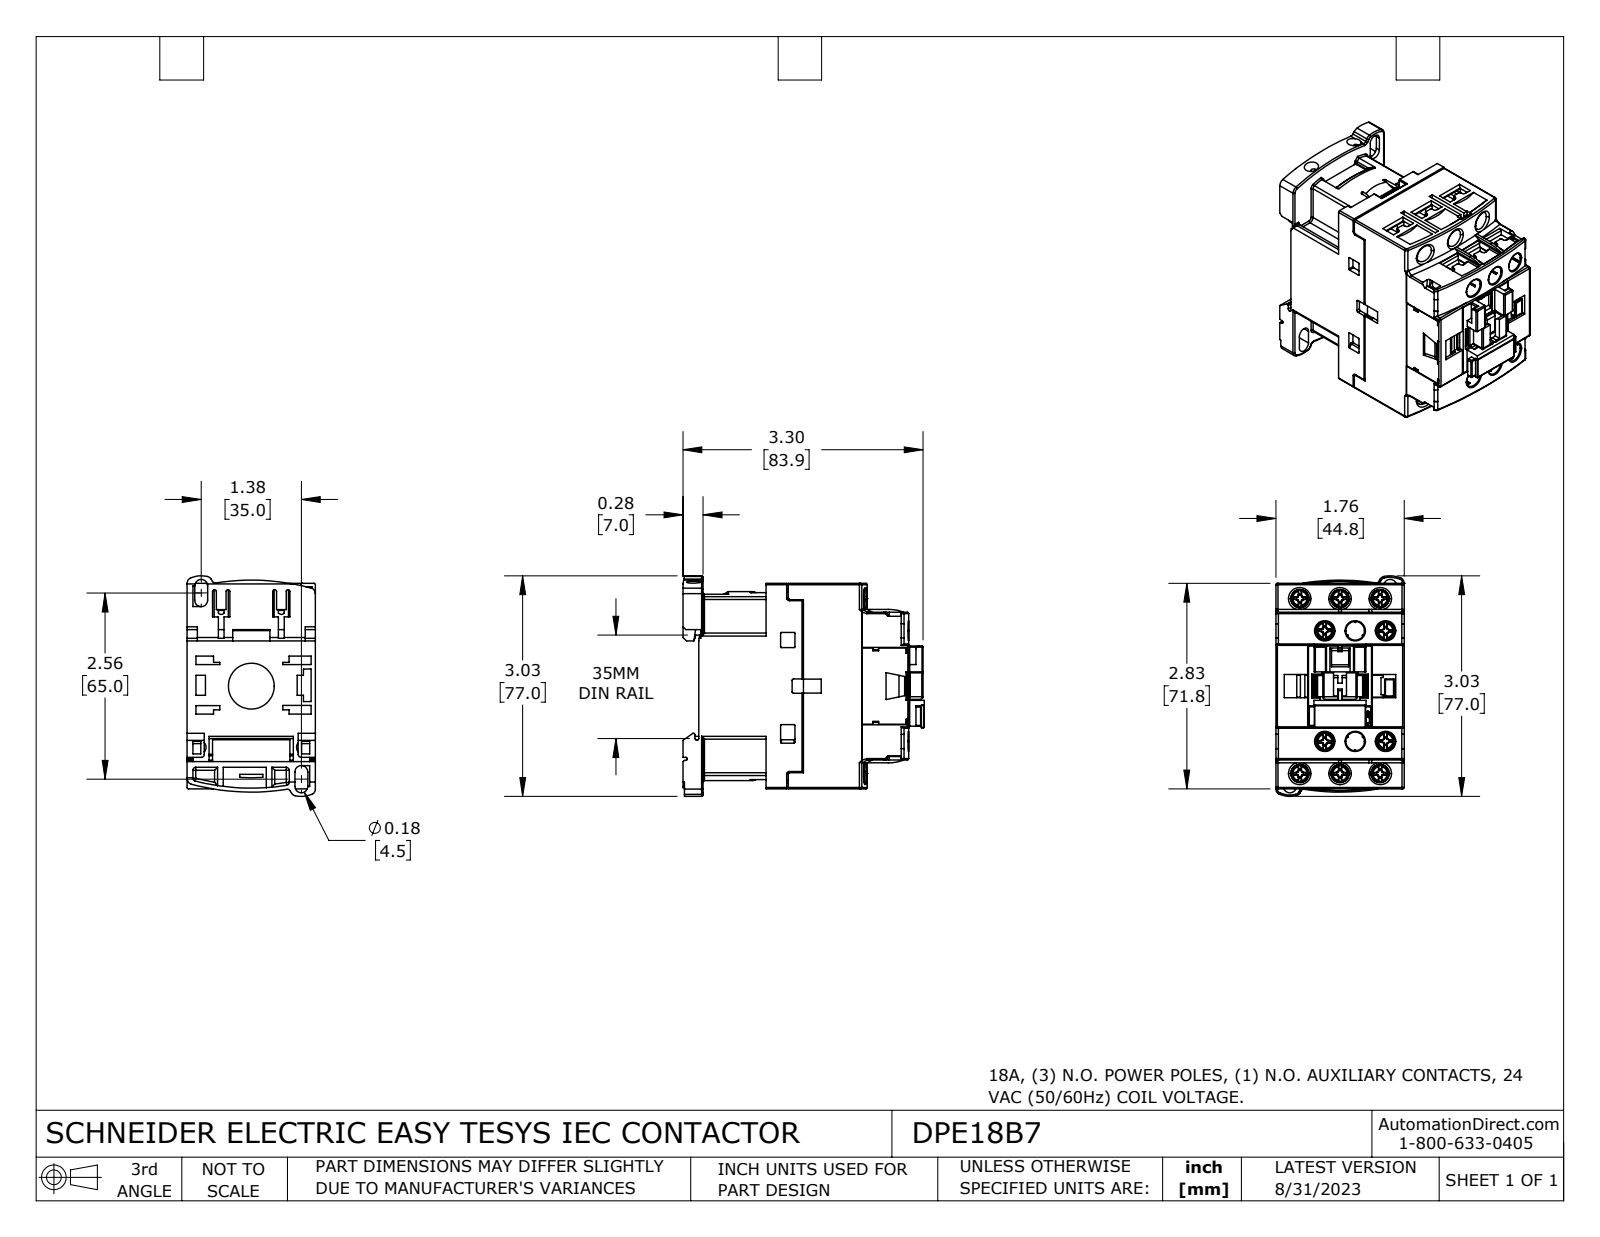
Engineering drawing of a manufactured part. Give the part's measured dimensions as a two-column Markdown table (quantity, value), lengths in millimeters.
| quantity | value |
| --- | --- |
| part name | DPE18B7 |
| STEP written by | SolidWorks 2021 (CONFIG_CONTROL_DESIGN) |
| units | millimeters |
| bodies | 20 solids, 3363 faces (2297 planar, 694 cylindrical, 372 other) |
| overall size | 84.3 × 77 × 45.3 |
| volume | 146 000 mm³ |
| surface area | 66 710 mm² |
| round holes (diameter × count) | 6.4 × 6, 6.5 × 6, 5 × 2, 4.2 × 1, 16 × 1 |
| round bosses / shafts (diameter × count) | 3.5 × 10, 2.7 × 10, 8 × 6 |
| partial cylindrical surfaces (radius × count) | 0.5 × 78, 0.3 × 64, 1 × 61, 0.2 × 42, 0.4 × 24, 16 × 9, 0.6 × 8, 2 × 7 |
| main face-to-face distances | 1.2, 44.8, 43.6, 8.2, 28.7, 20.5, 8.9, 70.6, 34.7, 28.4 |
| hole center spacings | 10.6, 12.4, 14, 14.2, 20, 22.3, 33.6, 40 |
